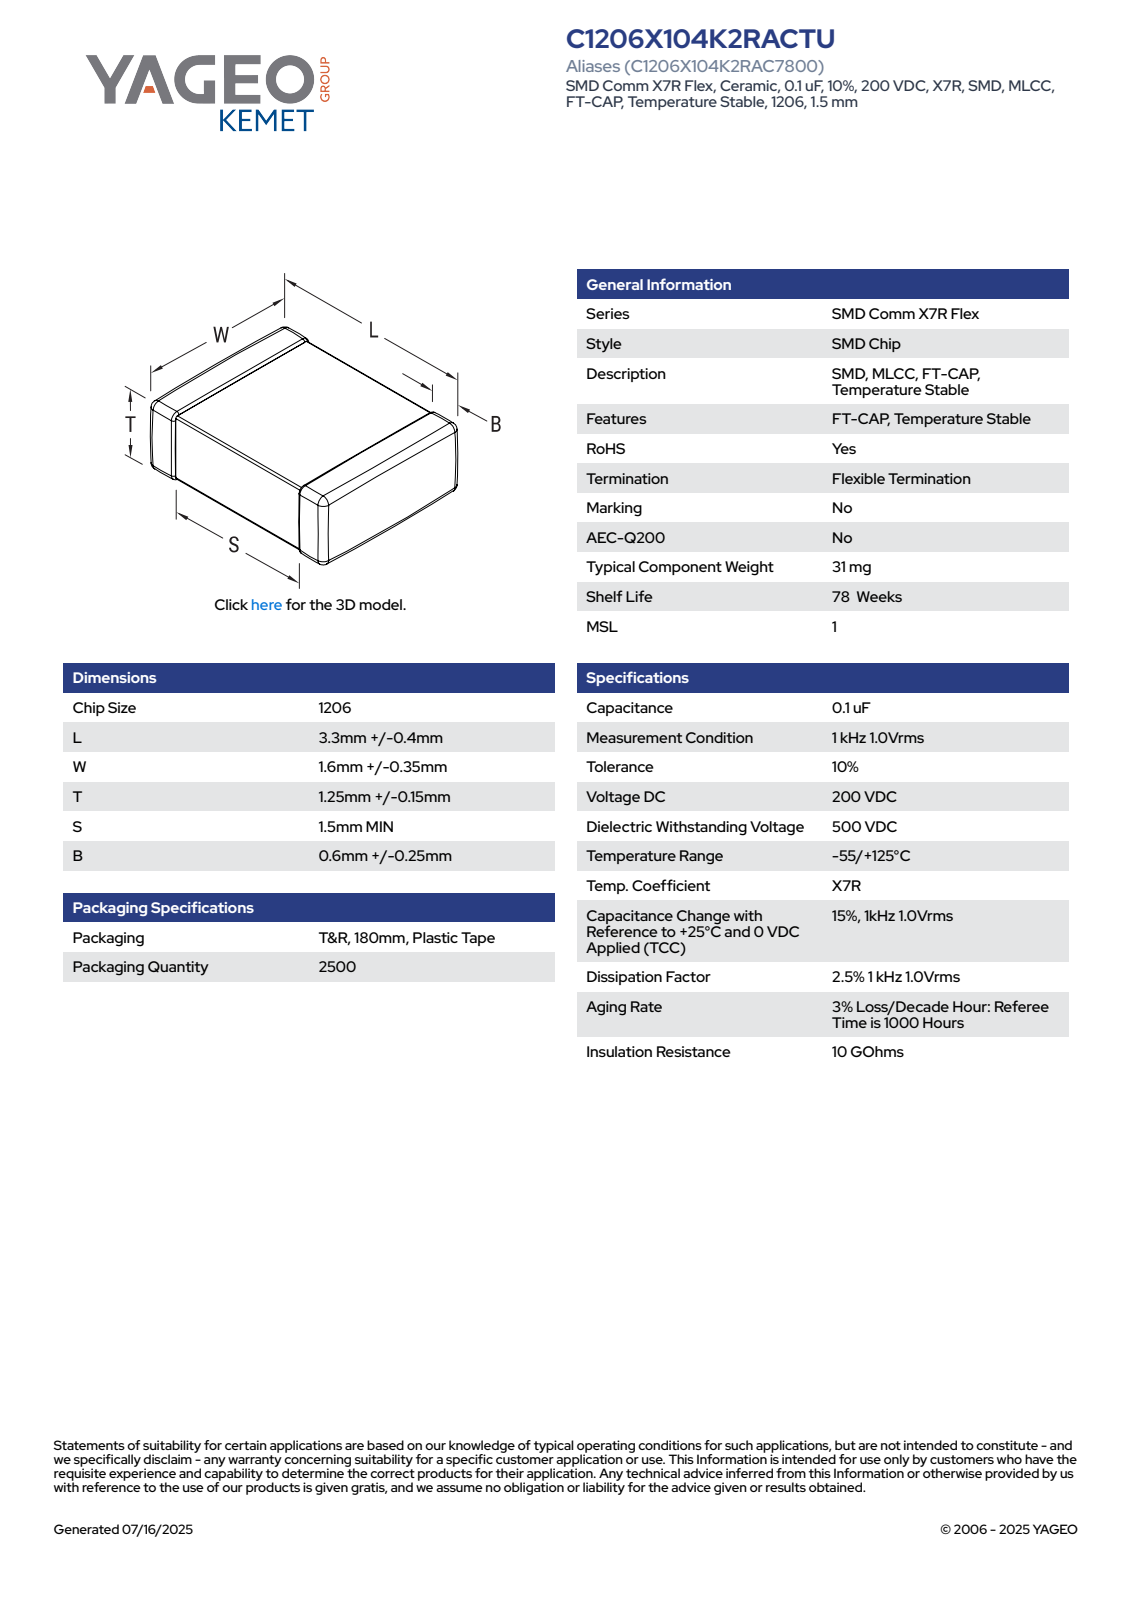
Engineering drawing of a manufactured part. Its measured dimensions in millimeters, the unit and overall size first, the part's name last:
Units: millimetres
Overall size (bounding box): 3.7 × 1.95 × 1.4
Main face-to-face distances: 1.36, 1.91, 1.32, 1.4, 1.87, 3.7, 1.95, 1.71, 1.99, 2
Volume: 10 mm³ · Surface area: 30 mm²
Bodies: 4 solids, 125 faces (71 planar, 38 cylindrical, 16 other)
Part name (STEP PRODUCT): CCS_CCSTD_1206_L3.7W1.95T1.4B0.6
STEP written by: SolidWorks 2021 (AUTOMOTIVE_DESIGN)
